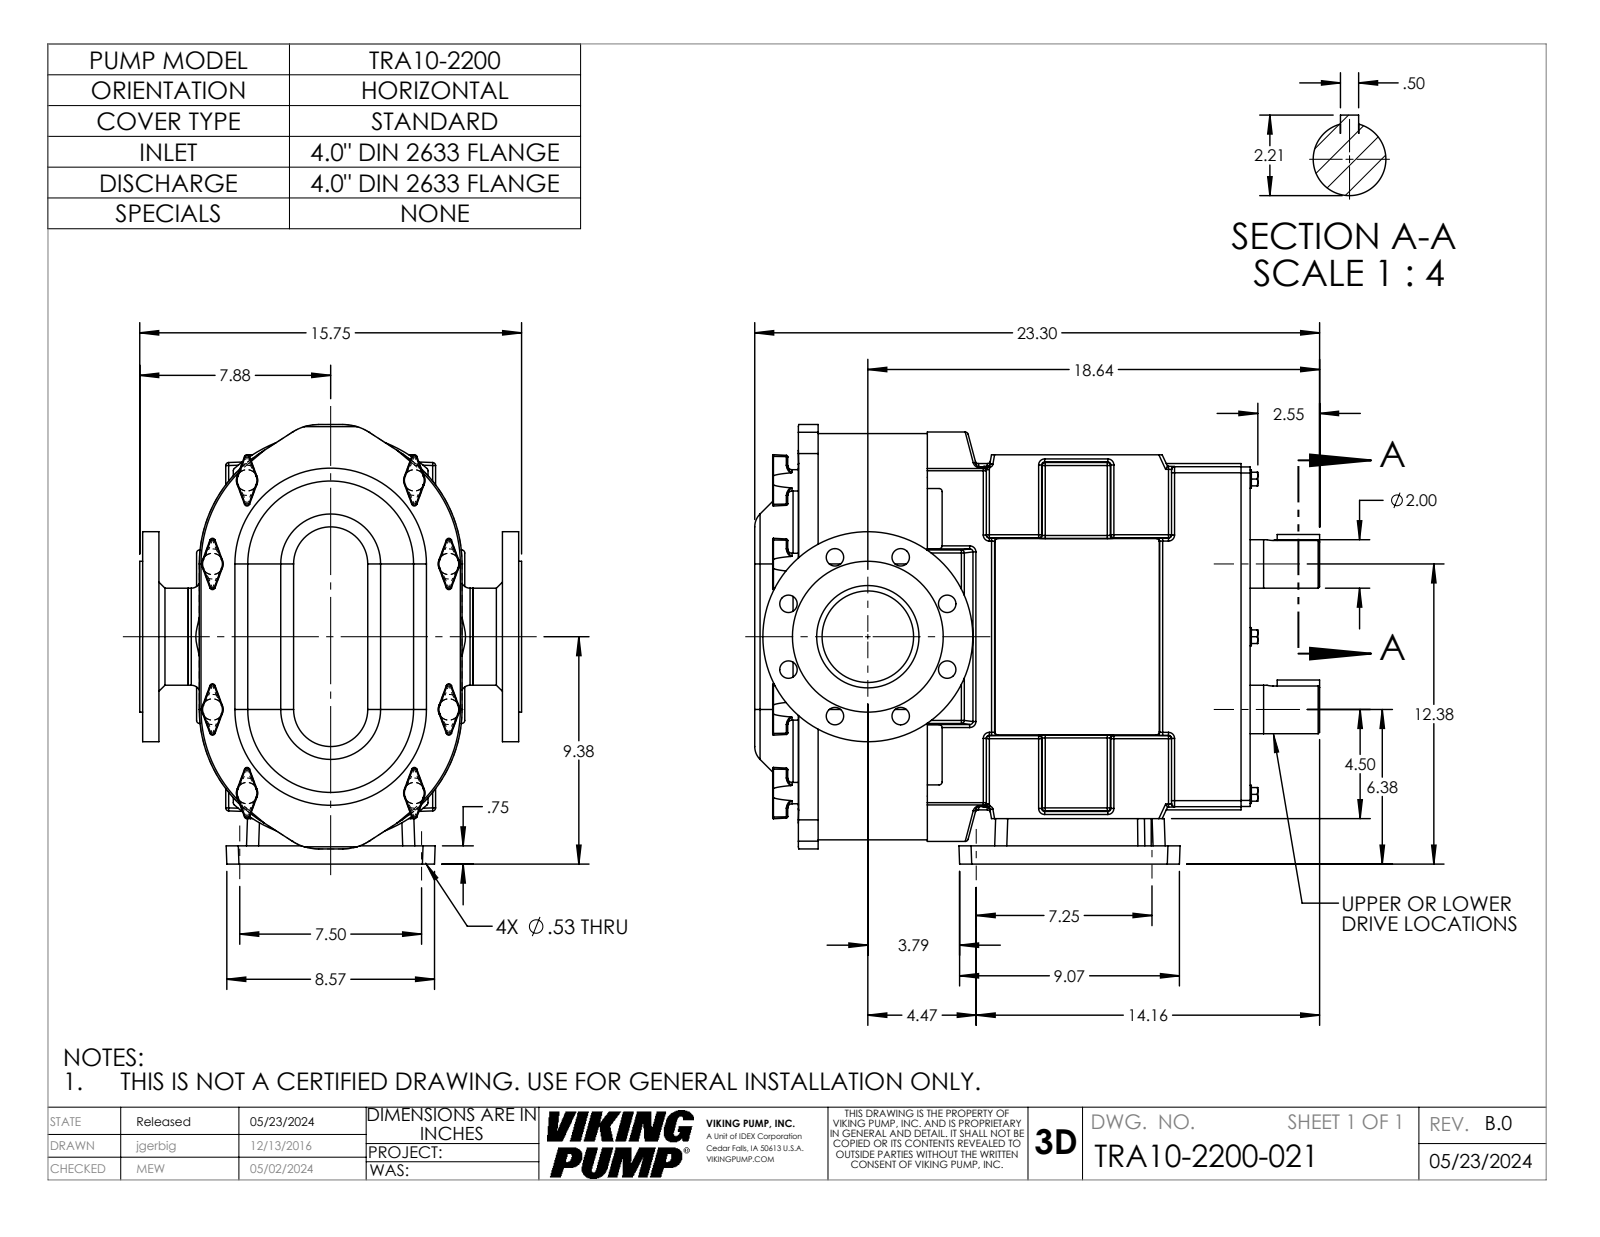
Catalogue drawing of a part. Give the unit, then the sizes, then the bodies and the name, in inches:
Units: inches
Overall size (bounding box): 23.301 × 18.125 × 15.75
Round holes (diameter × count): ⌀0.72 ×8, ⌀0.531 ×4, ⌀3.775 ×1, ⌀3.775 ×1, ⌀4.22 ×1
Round bosses / shafts (diameter × count): ⌀0.88 ×8, ⌀0.75 ×6, ⌀1.999 ×2, ⌀8.66 ×1, ⌀6.22 ×1, ⌀4 ×1
Partial cylindrical surfaces — rounded edges, fillets, slot ends (radius × count): R0.125 ×138, R0.03 ×32, R0.06 ×32, R0.25 ×16, R0.5 ×16, R0.75 ×4, R2 ×4, R5.375 ×2
Main face-to-face distances: 4.505, 0.484, 8.516, 17.82, 13.315, 2.585, 3.069, 11.101, 11.585, 5.365
Hole centre spacings: 3.543, 5.011, 6.547, 2.712, 2.712, 7.087, 7.25, 7.5
Volume: 2 682 in³ · Surface area: 2 433 in²
Bodies: 5 solids, 958 faces (266 planar, 380 cylindrical, 312 other)
Part name (STEP PRODUCT): 2200DIN2633-40; TRA10-2200-GEARBOX-H; TRA10-2200-COVER-STD; TRA10-2200-021 (+1 more)
STEP written by: SolidWorks 2023 (AUTOMOTIVE_DESIGN)
